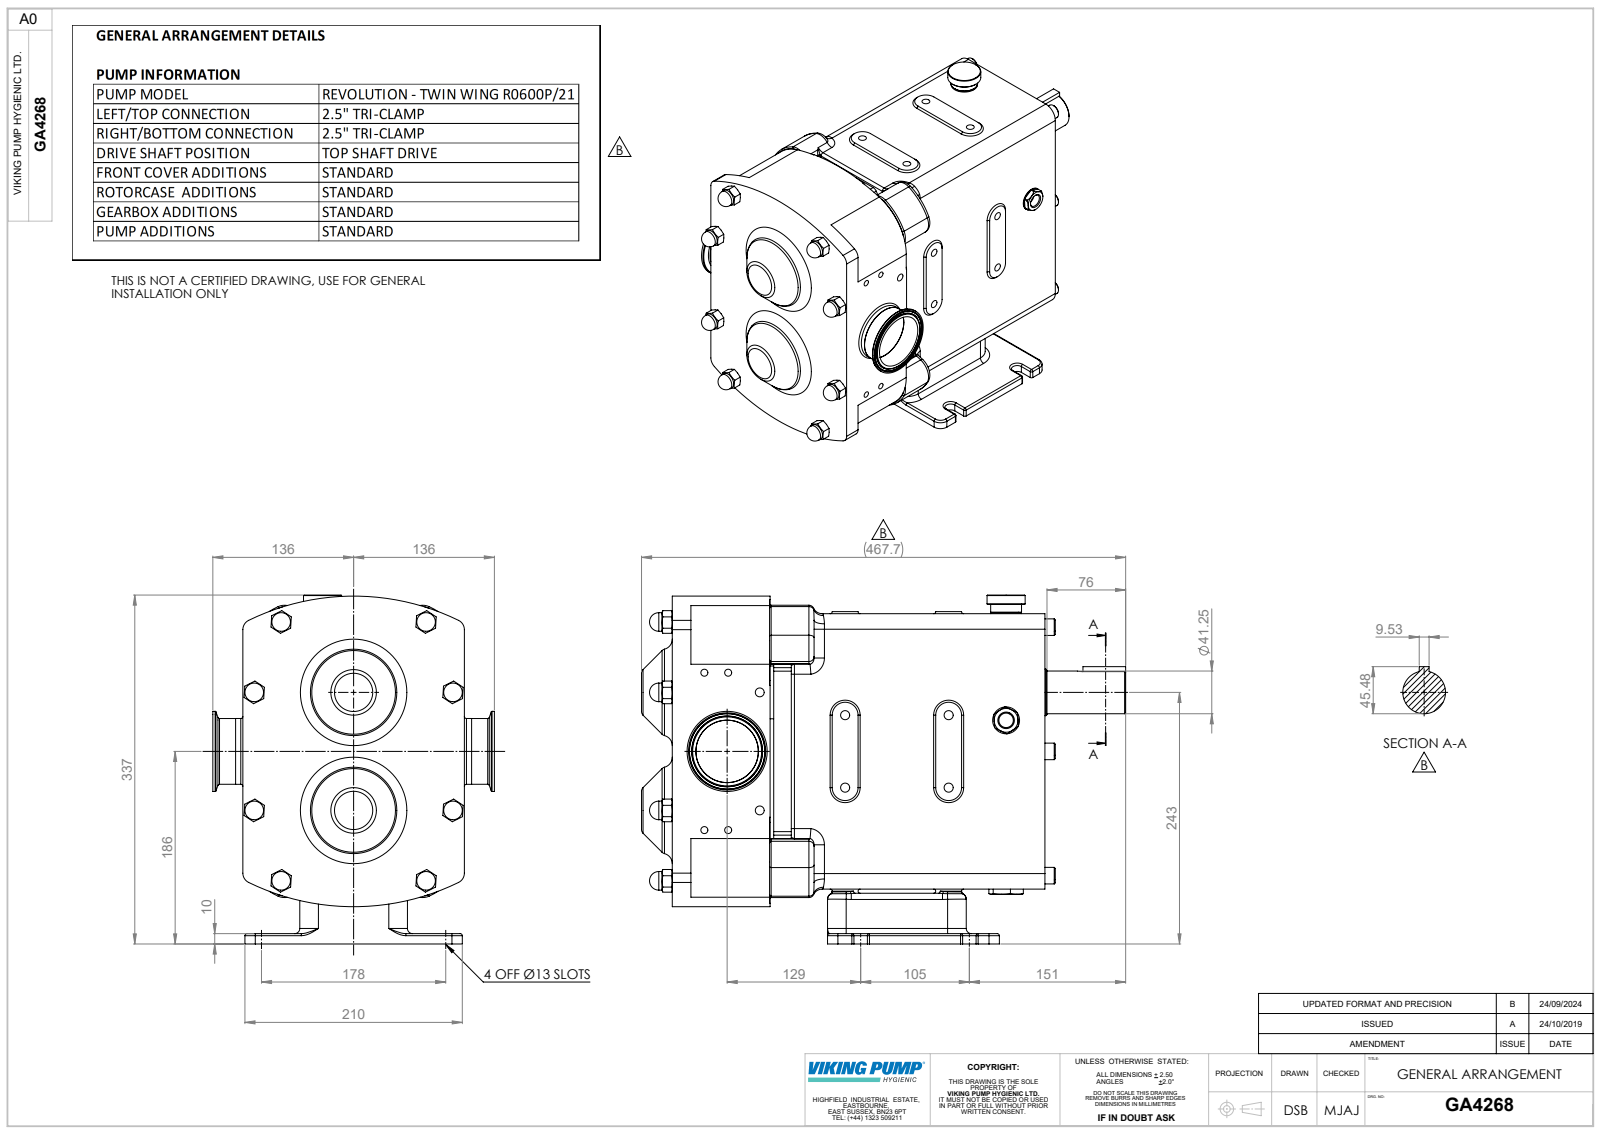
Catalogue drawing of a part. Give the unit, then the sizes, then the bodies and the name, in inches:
Units: inches
Overall size (bounding box): 18.413 × 13.268 × 10.709
Round holes (diameter × count): ⌀0.346 ×8, ⌀0.268 ×4, ⌀0.339 ×2, ⌀0.551 ×1, ⌀1.331 ×1, ⌀2.374 ×1, ⌀2.376 ×1
Round bosses / shafts (diameter × count): ⌀0.709 ×8, ⌀0.63 ×6, ⌀3.047 ×1, ⌀2.504 ×1, ⌀2.5 ×1, ⌀2.008 ×1, ⌀1.772 ×1, ⌀1.624 ×1
Partial cylindrical surfaces — rounded edges, fillets, slot ends (radius × count): R0.079 ×38, R0.394 ×30, R0.197 ×19, R0.232 ×8, R0.591 ×8, R0.709 ×8, R0.118 ×4, R0.236 ×4
Main face-to-face distances: 5.984, 3.72, 10.453, 14.173, 0.138, 10.315, 3.858, 1.693, 10.472, 1.22
Hole centre spacings: 2.756, 3.937, 4.806, 9.43, 0.906, 1.415, 2.194, 2.235
Volume: 1 040 in³ · Surface area: 1 084 in²
Bodies: 3 solids, 962 faces (299 planar, 286 cylindrical, 377 other)
Part name (STEP PRODUCT): GA4268; Copy of RA94-5121-44M^GA4268; Copy of R0600 CPP H TSD^GA4268
STEP written by: SolidWorks 2023 (AUTOMOTIVE_DESIGN)
